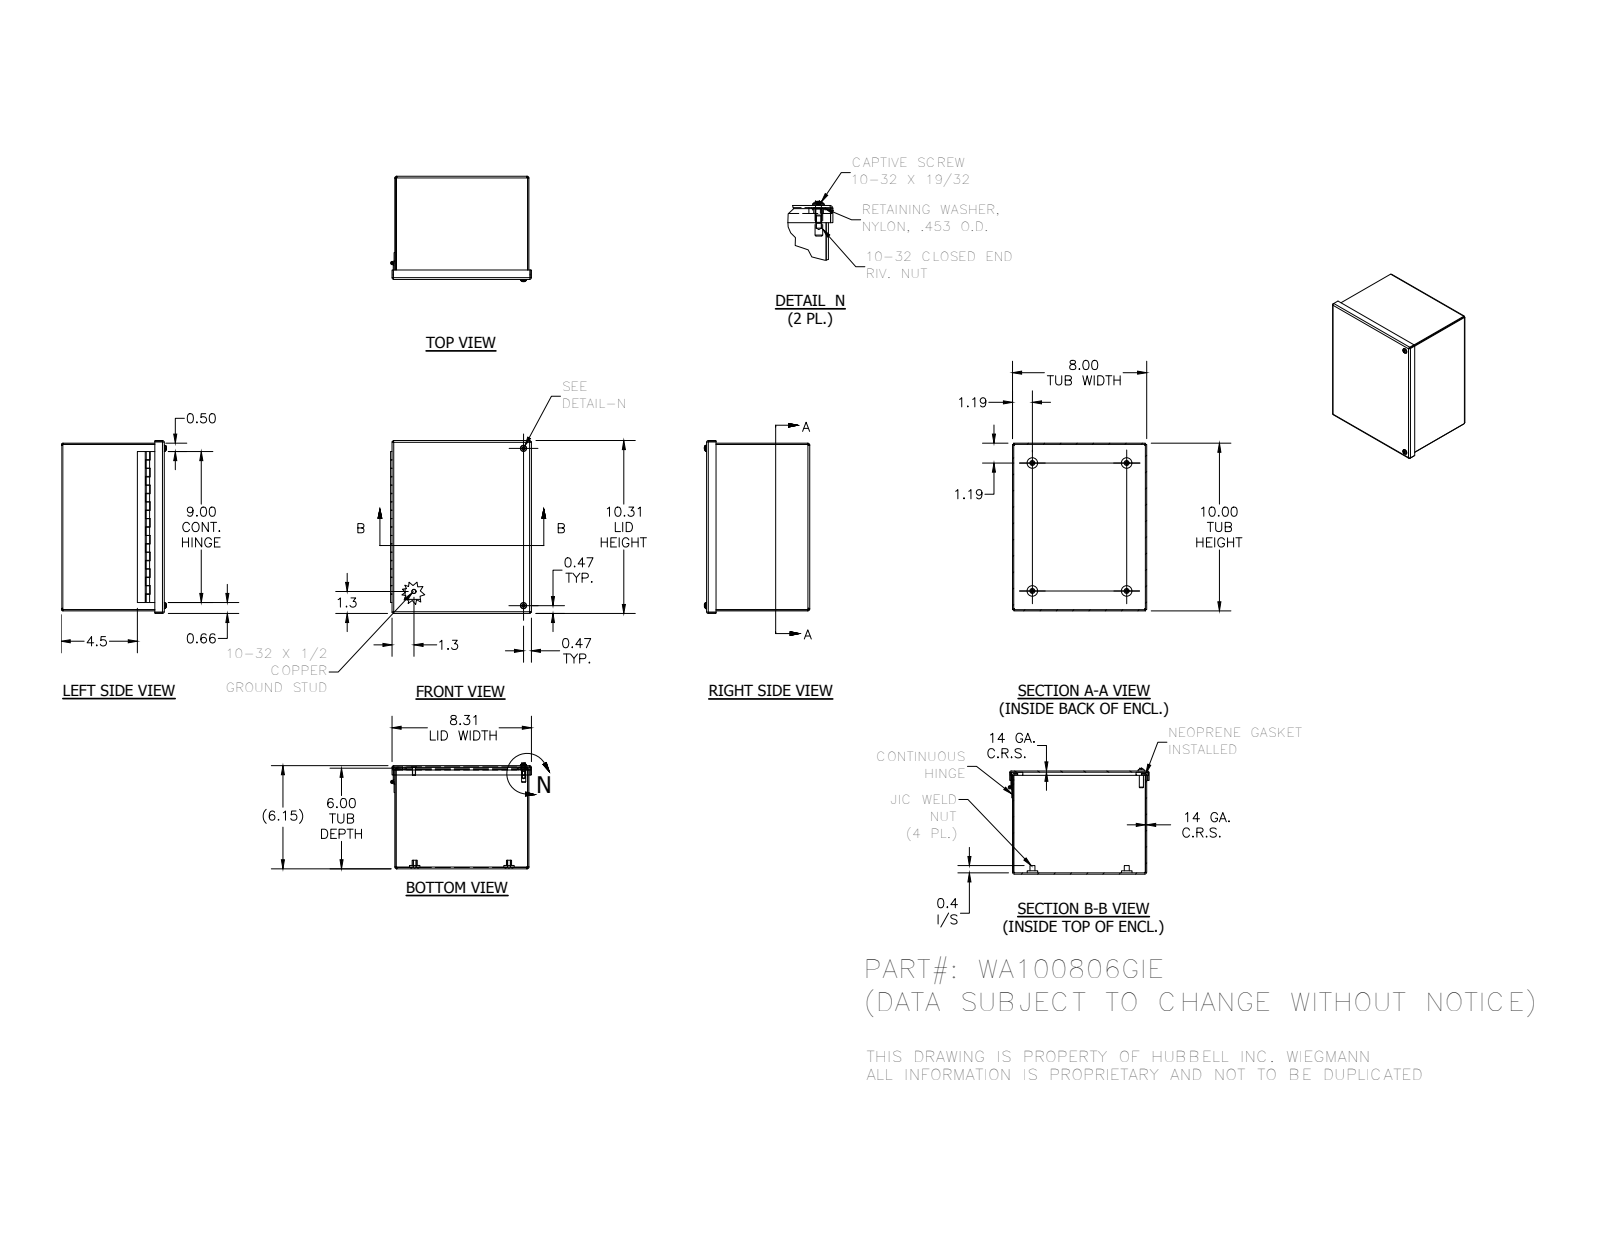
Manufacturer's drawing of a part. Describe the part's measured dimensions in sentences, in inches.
The part is named "WA100806GIEBKP; 3499; 328122LH; 328122P (+8 more)". Its 3-D file was written by "Autodesk Inventor 2014 (AUTOMOTIVE_DESIGN)". It is 18 solids with 465 faces: 269 planar, 121 cylindrical and 75 other. Overall it measures 10.313 by 8.397 by 6.282 inches. Its volume is 35.28 cubic inches and its surface area 918.2 square inches. Round holes: 6 of diameter 0.156, 4 of diameter 0.257, 4 of diameter 0.313, 2 of diameter 0.196, 2 of diameter 0.278, 2 of diameter 0.281, 1 of diameter 0.117. Round bosses or shafts: 4 of diameter 0.625, 4 of diameter 0.3, 3 of diameter 0.19, 2 of diameter 0.453, 2 of diameter 0.406, 2 of diameter 0.373, 2 of diameter 0.248, 1 of diameter 0.25. Partial cylindrical surfaces (rounded edges, fillets, slot ends): 12 of radius 0.031, 12 of radius 0.105, 8 of radius 0.07, 2 of radius 0.089. The main face-to-face distances are 0.074, 6.078, 7.926, 9.926, 6.004, 6.152, 8, 7.852, 10, 9.852. The hole center spacings are 9.375, 1.237, 6.559, 7.375, 9.374, 7.386, 8.545, 10.7.
